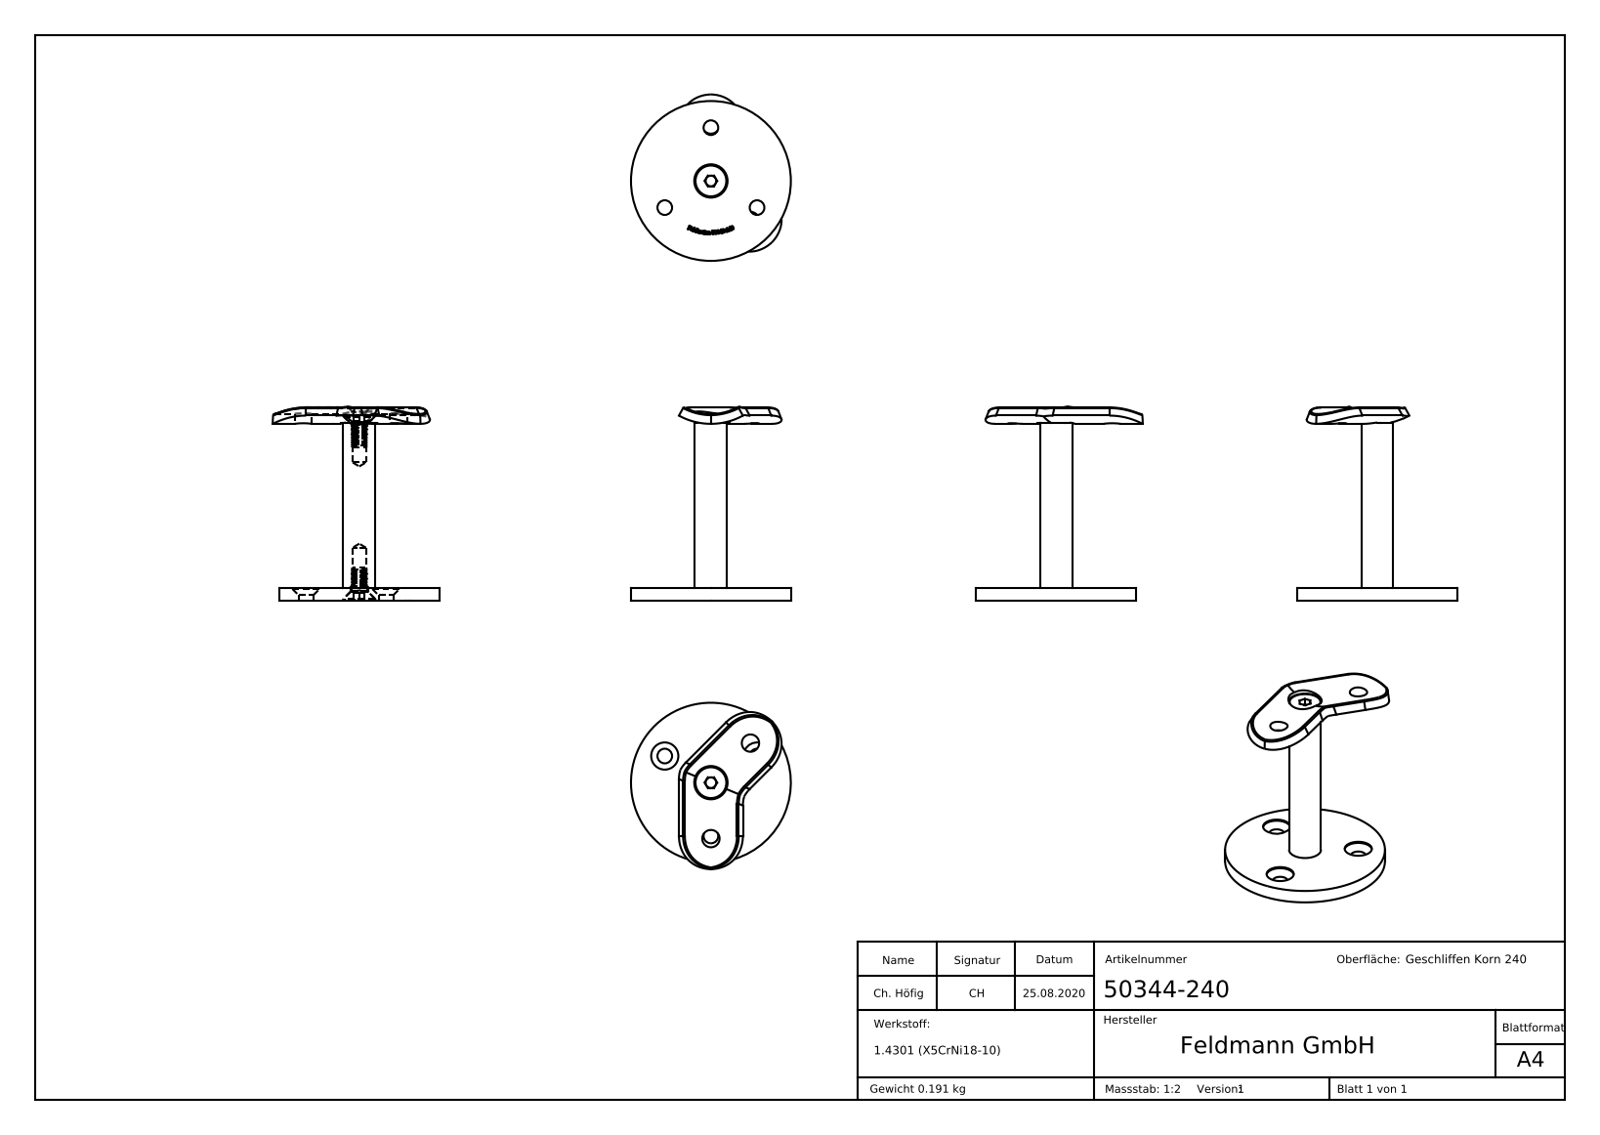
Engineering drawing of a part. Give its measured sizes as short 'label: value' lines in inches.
name: 5034X-240 Teil1_50343-240 Teil1; 5034X-240 Teil2_5034X-240 Teil2; 50344-240; 50344-240 Teil3_50344-240 Teil3 (+1 more)
written by: SolidWorks 2015 (CONFIG_CONTROL_DESIGN)
unit: in
bodies: 5 solids, 468 faces (163 planar, 85 cylindrical, 220 other)
size: 2.871 × 2.461 × 2.362
volume: 1.384 in³; area: 21.56 in²
holes: 5× ⌀0.217, 3× ⌀0.413, 1× ⌀0.197, 1× ⌀0.256, 1× ⌀0.315, 1× ⌀0.48, 1× ⌀0.492
bosses: 1× ⌀2.362, 1× ⌀0.472, 1× ⌀0.456, 1× ⌀0.236
rounds: 4× R0.02, 4× R0.492, 2× R0.394, 2× R0.835, 2× R0.992
face distances: 0.157, 2.638, 2.48, 2.748, 2.591, 0.11, 0.018, 0.14, 2.62, 2.73
hole spacings: 0.886, 0.827, 1.483, 1.534, 0.059, 0.231, 1.359, 1.528
